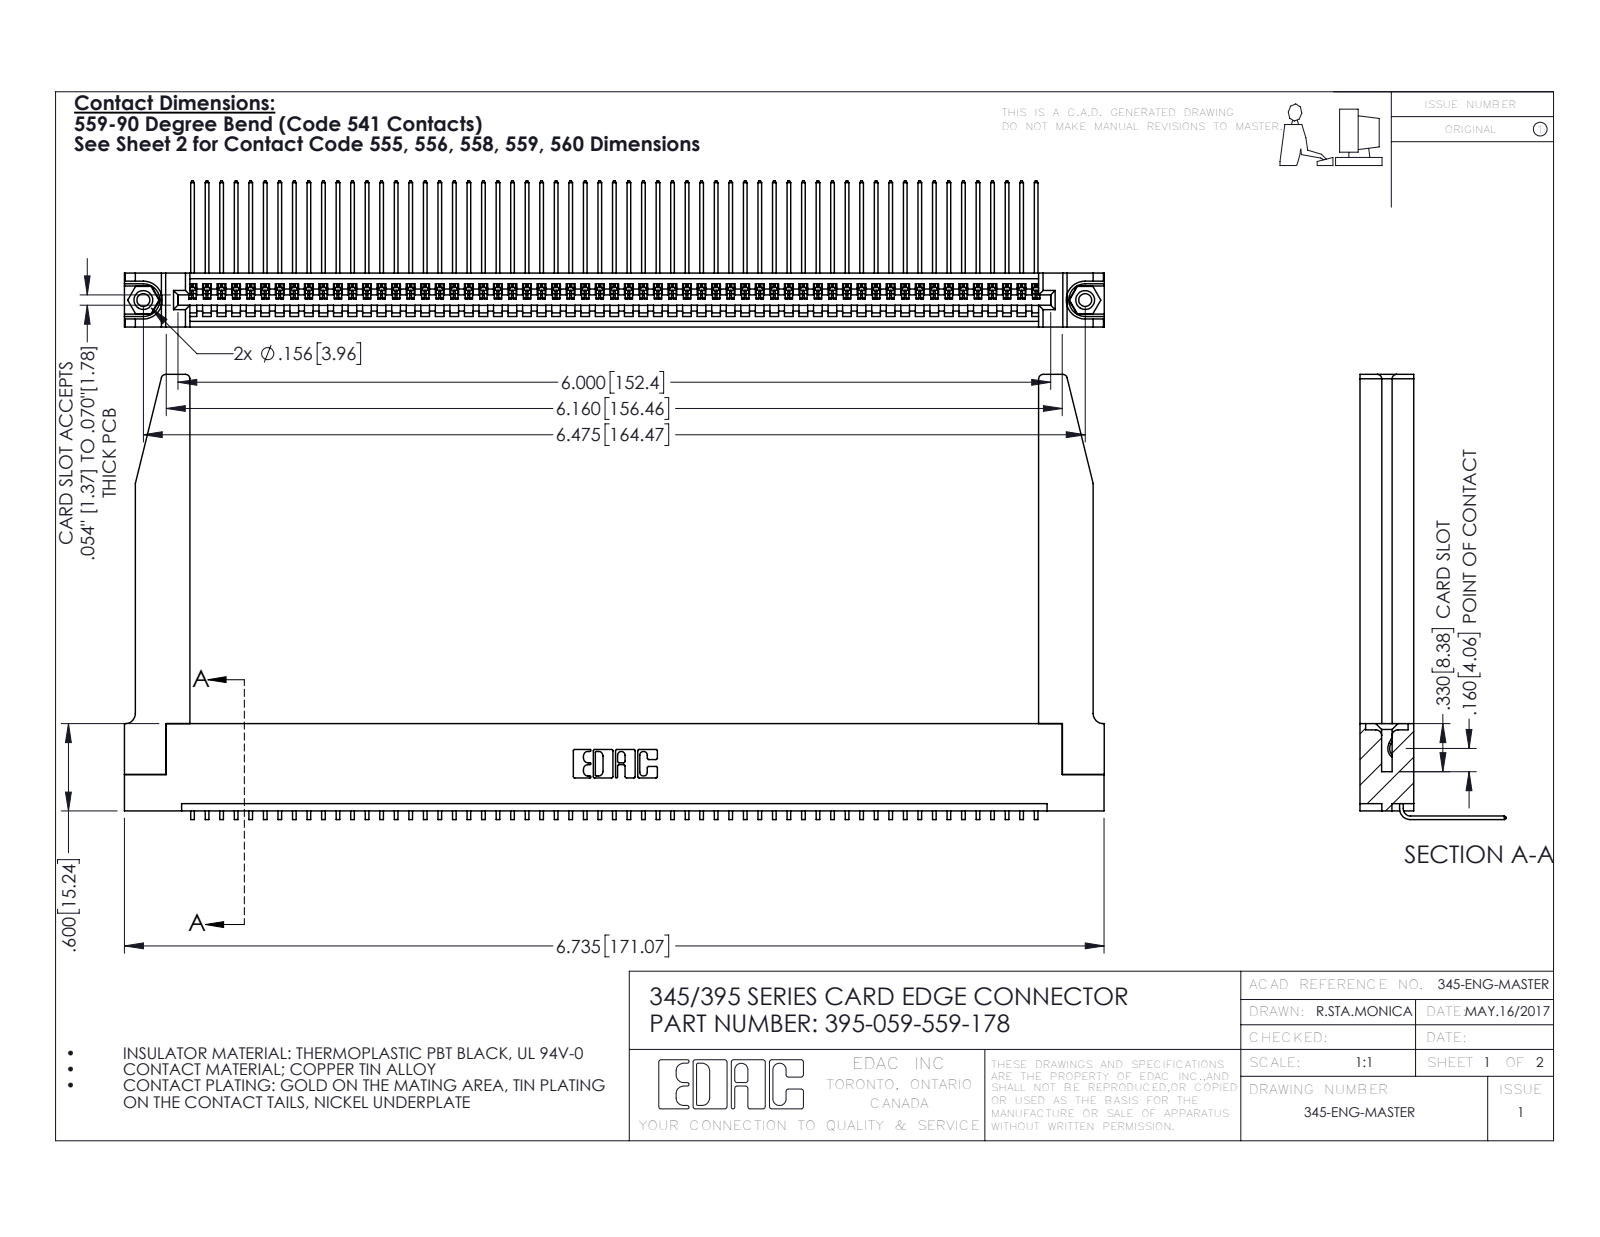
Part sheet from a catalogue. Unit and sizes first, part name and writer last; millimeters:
Units: millimetres
Overall size (bounding box): 171.1 × 77.7 × 25.5
Round holes (diameter × count): ⌀2.3 ×2, ⌀3.2 ×2, ⌀4 ×2, ⌀1.6 ×1
Round bosses / shafts (diameter × count): ⌀3.9 ×2
Partial cylindrical surfaces — rounded edges, fillets, slot ends (radius × count): R0.2 ×118, R0.3 ×22, R0.8 ×8, R0.2 ×6, R0.8 ×6, R0.7 ×3, R0.8 ×2, R1 ×2
Main face-to-face distances: 9.4, 1.8, 7.6, 5.1, 2.5, 6.9, 0.6, 5.7, 3.8, 3.8
Hole centre spacings: 6.9, 158.5, 164.5
Volume: 24 350 mm³ · Surface area: 30 270 mm²
Bodies: 64 solids, 3900 faces (2700 planar, 1148 cylindrical, 52 other)
Part name (STEP PRODUCT): 345 Part_Flush Mounting Lugs - 0.156 Dia-TH; 395-059-559-178; 345-250-001_345-250-001-102; 345-220-078_345-220-078 (+1 more)
STEP written by: SolidWorks 2016 (CONFIG_CONTROL_DESIGN)
